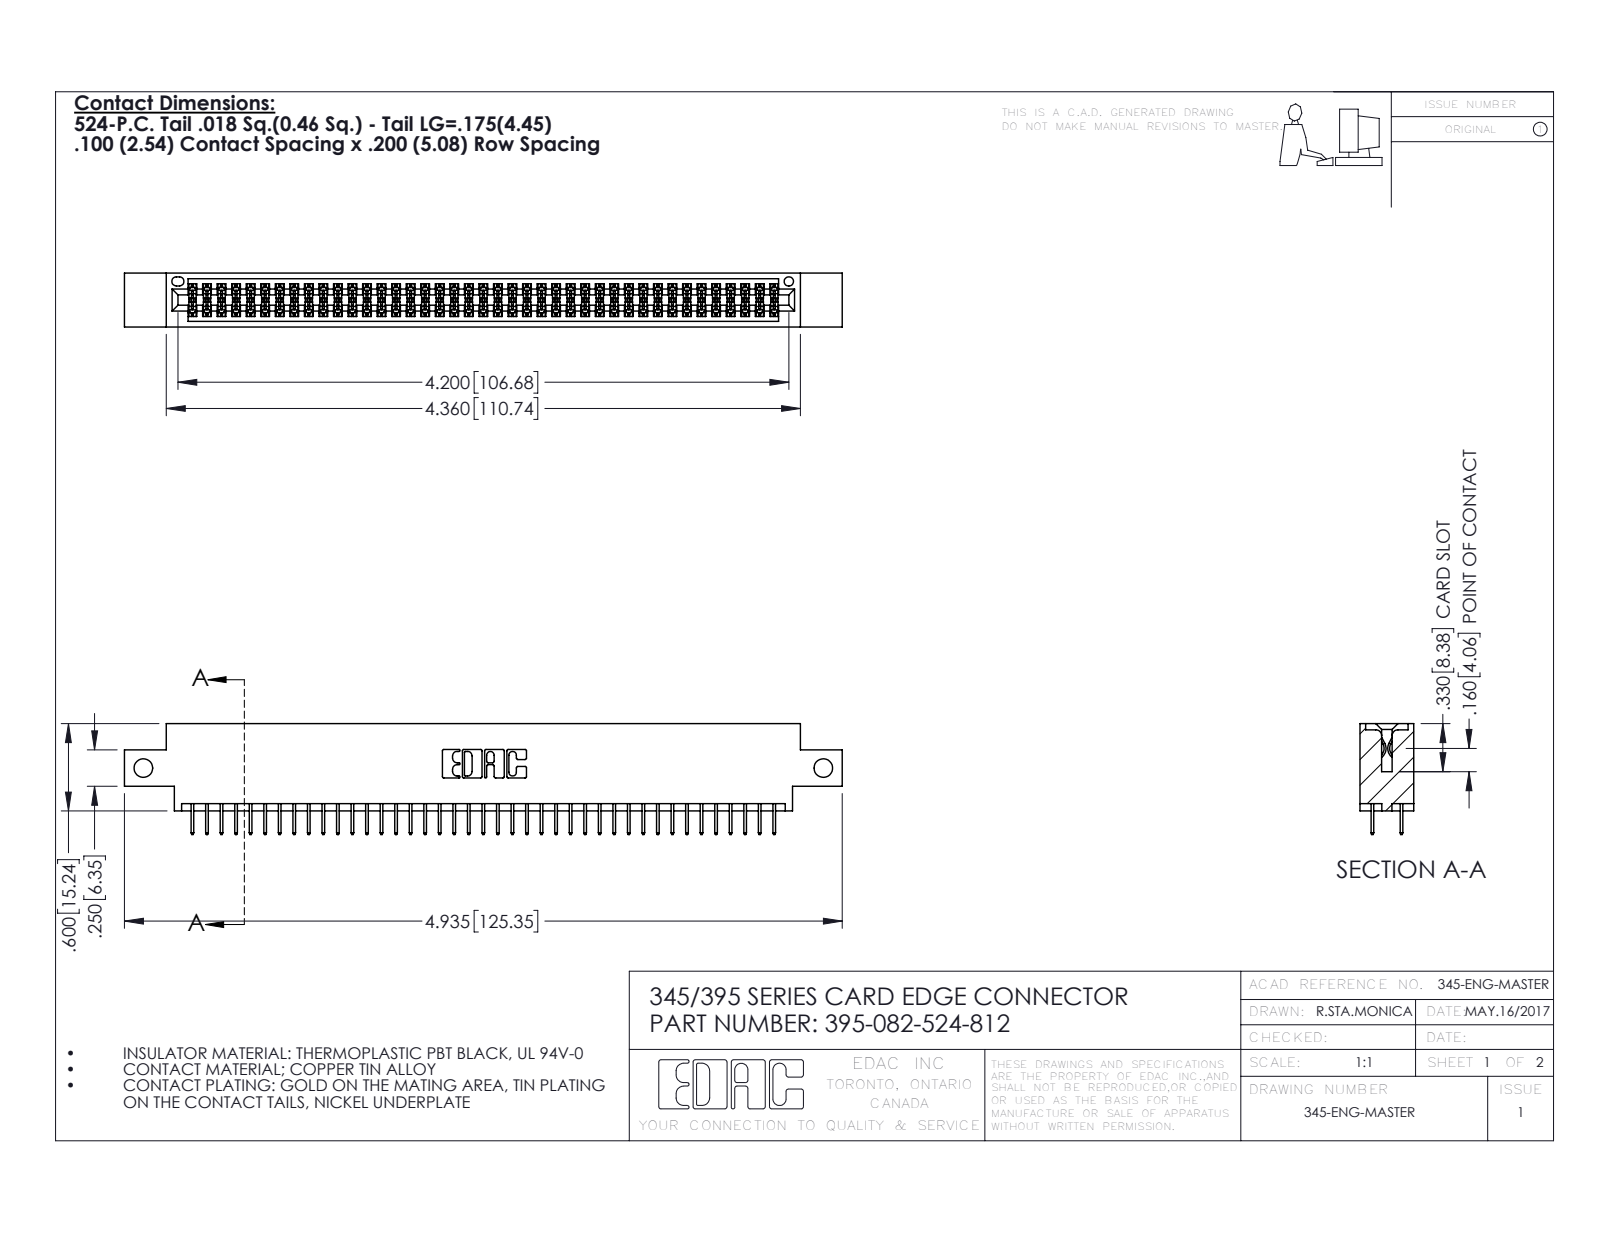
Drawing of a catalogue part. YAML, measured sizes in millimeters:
part_name: "395-082-524-812; 345 Part_0.170 Offset - Side Mount; 345-292-001_345-293-124"
step_written_by: "SolidWorks 2016 (CONFIG_CONTROL_DESIGN)"
units: millimeters
bodies: {solids: 83, faces: 4558, planar: 3282, cylindrical: 1276, other: 0}
overall_size: [125.3, 19.4, 9.4]
volume: 11800
surface_area: 17170
round_holes:
  - {diameter: 3.3, count: 2}
  - {diameter: 1.6, count: 1}
partial_cylinders:
  - {radius: 0.2, count: 123}
  - {radius: 0.3, count: 22}
  - {radius: 0.2, count: 6}
  - {radius: 0.8, count: 6}
  - {radius: 0.7, count: 3}
  - {radius: 0.4, count: 2}
  - {radius: 0.5, count: 2}
  - {radius: 0.6, count: 2}
face_to_face_distances: [1.8, 7.6, 9.4, 5.1, 2.5, 6.9, 0.6, 5.7, 4.4, 1.8]
hole_center_spacings: [118.7]
